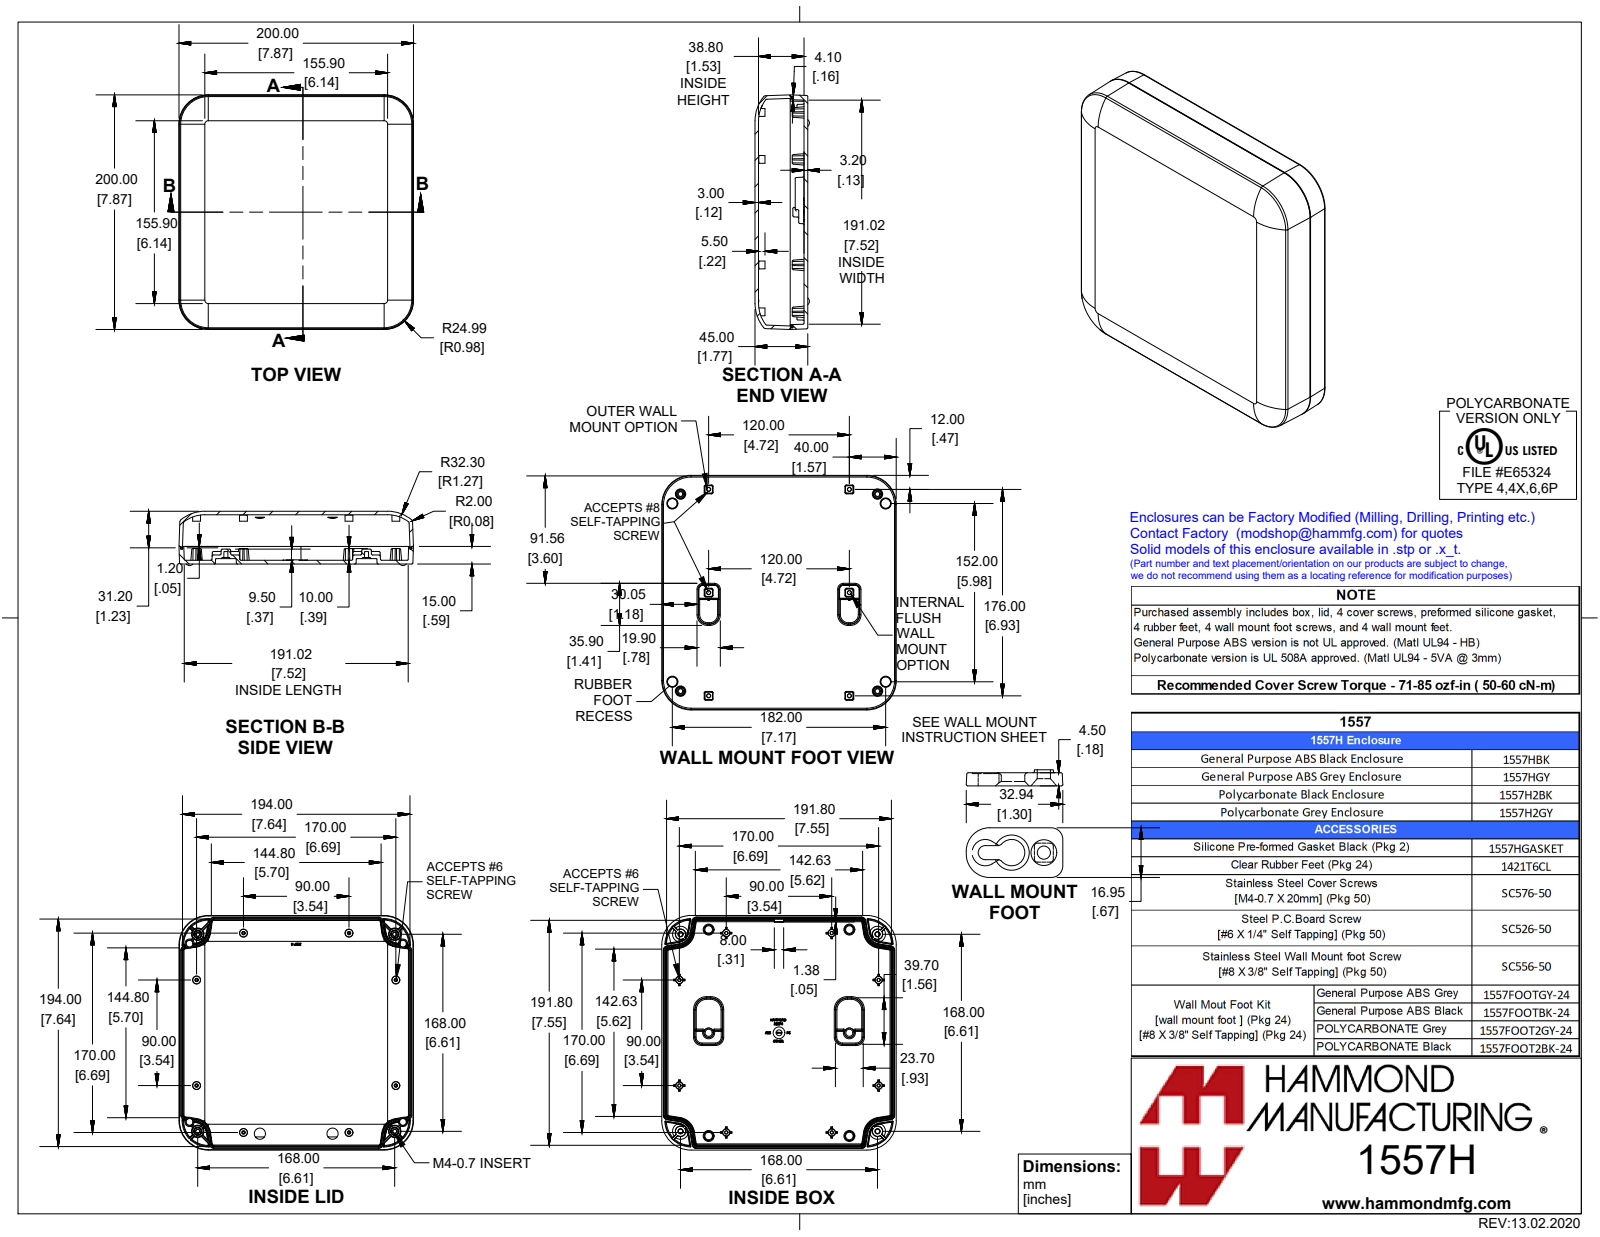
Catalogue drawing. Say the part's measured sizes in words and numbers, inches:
The part is named "Wall Mount Foot; IN-M4 (insert M4-0.7X5.75mm SS) KNURLS; 1557H Gasket; SC576 (screw M4-0.7X 20mm PN) (+5 more)". Its 3-D file was written by "SolidWorks 2019 (CONFIG_CONTROL_DESIGN)". It is 23 solids with 2846 faces: 965 planar, 578 cylindrical and 1303 other. Overall it measures 9.014 by 7.874 by 1.949 inches. Its volume is 22.44 cubic inches and its surface area 395 square inches. Round holes: 4 of diameter 0.128, 4 of diameter 0.177. Round bosses or shafts: 12 of diameter 0.071, 4 of diameter 0.313, 4 of diameter 0.303, 4 of diameter 0.25, 4 of diameter 0.218, 4 of diameter 0.21, 4 of diameter 0.165, 4 of diameter 0.153. Partial cylindrical surfaces (rounded edges, fillets, slot ends): 101 of radius 0.02, 78 of radius 0.039, 12 of radius 0.157, 8 of radius 0.008, 8 of radius 0.012, 8 of radius 0.016, 8 of radius 0.059, 8 of radius 0.083. The main face-to-face distances are 0.118, 0.126, 1.654, 1.528, 1.772, 1.646, 7.748, 7.867, 0.161, 7.587. The hole center spacings are 0.958, 5.672, 6.614, 6.837, 8.831, 4.724, 6.929, 8.387.
